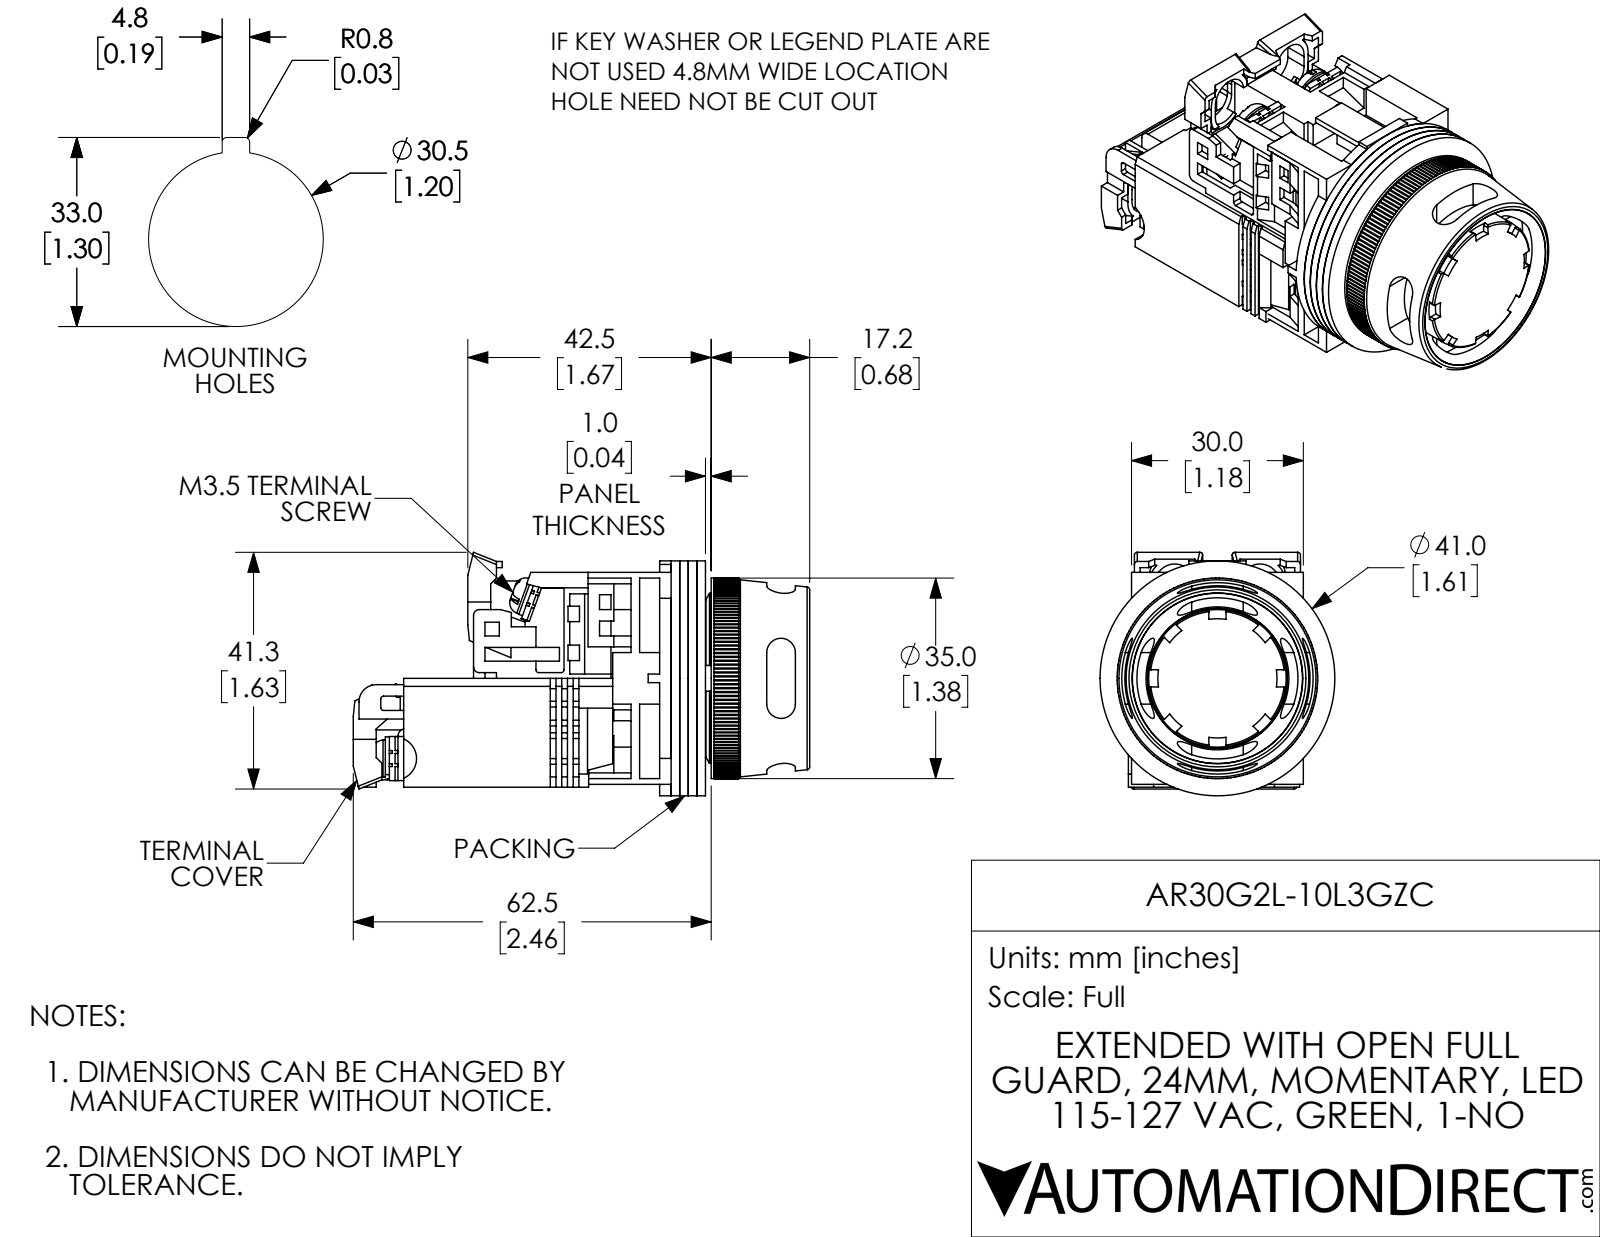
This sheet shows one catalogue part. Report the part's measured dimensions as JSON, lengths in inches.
{"part_name": "AR30G2L-10L3GZC", "step_written_by": "SolidWorks 2017 (AUTOMOTIVE_DESIGN)", "units": "inches", "bodies": {"solids": 27, "faces": 2102, "planar": 1483, "cylindrical": 474, "other": 145}, "overall_size": [3.138, 1.673, 1.614], "volume_in3": 2.906, "surface_area_in2": 66.69, "round_holes": [[0.138, 6], [0.142, 4], [0.118, 3], [0.472, 1], [0.709, 1], [0.728, 1], [0.787, 1], [0.945, 1], [1.252, 1]], "round_bosses_or_shafts": [[0.26, 4], [0.138, 2], [1.614, 1], [1.378, 1], [1.181, 1], [0.866, 1], [0.776, 1], [0.551, 1]], "partial_cylinders_radius": [[0.01, 160], [0.059, 17], [0.012, 16], [0.02, 13], [0.098, 4], [0.138, 4], [0.177, 4], [0.039, 2]], "face_to_face_distances": [0.059, 0.118, 0.177, 0.039, 0.748, 0.276, 0.079, 1.417, 0.689, 0.138], "hole_center_spacings": [0.579, 0.02, 0.274, 0.32, 0.325, 0.583, 0.583, 0.61]}
